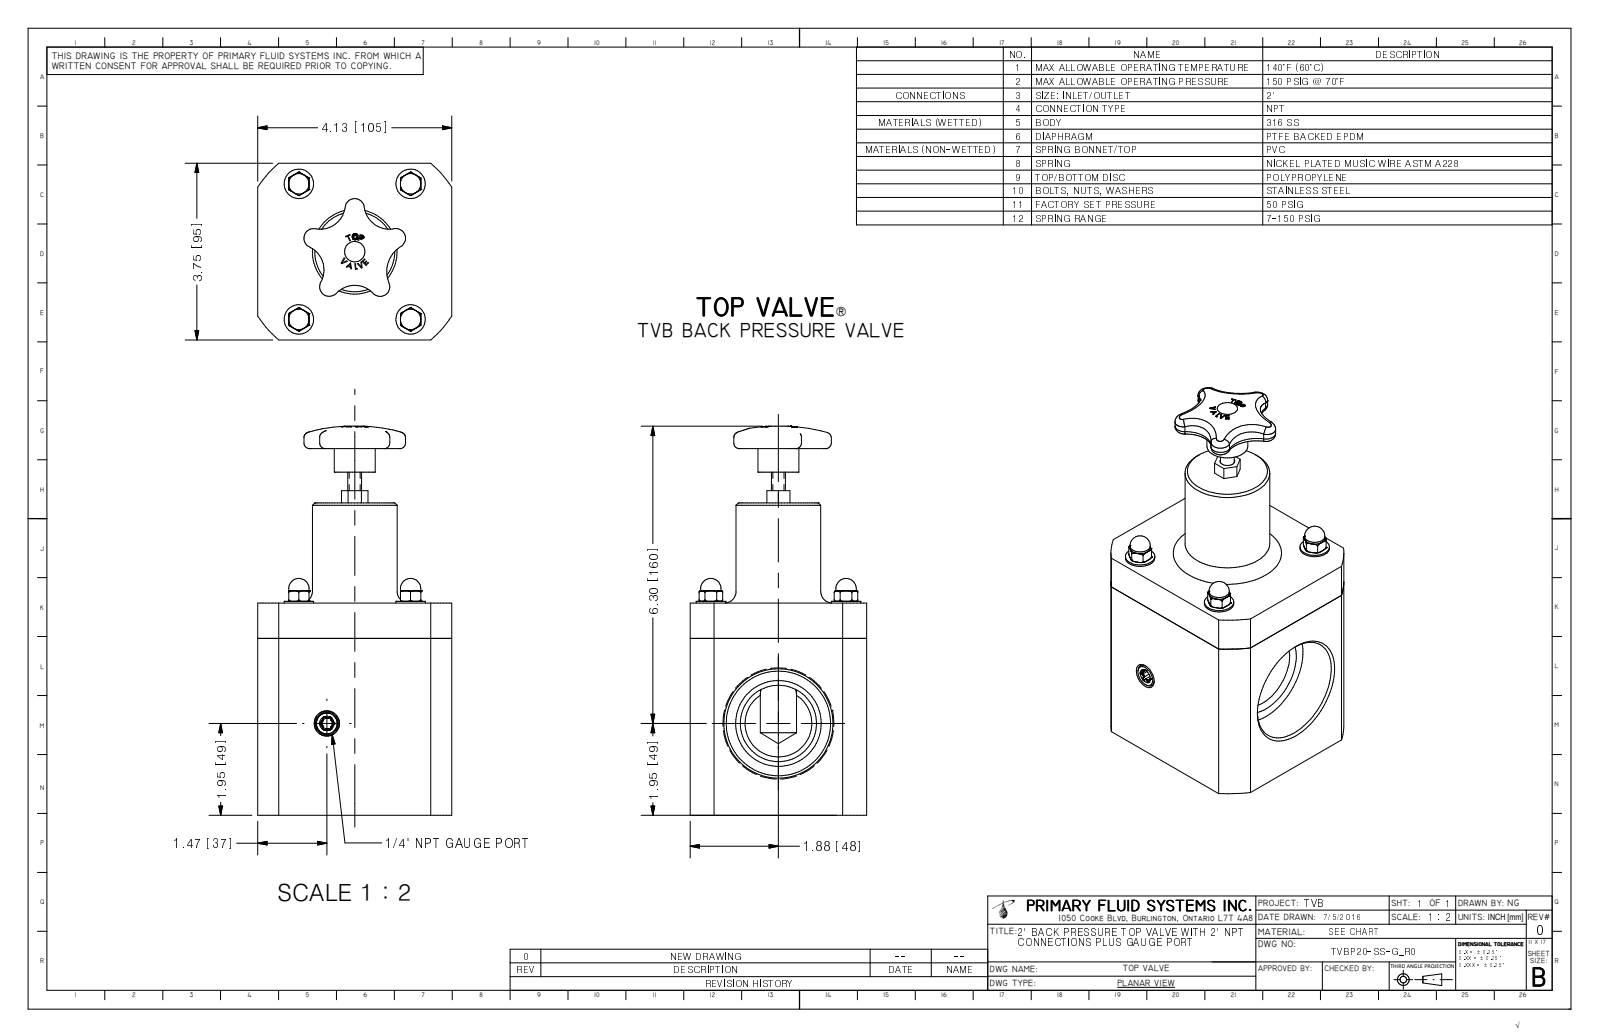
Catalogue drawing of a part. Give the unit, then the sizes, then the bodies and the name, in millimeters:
Units: millimetres
Overall size (bounding box): 209.6 × 104.8 × 95.3
Round holes (diameter × count): ⌀4.4 ×4, ⌀56.4 ×1
Round bosses / shafts (diameter × count): ⌀15.9 ×4, ⌀11 ×4, ⌀9.5 ×4, ⌀45.7 ×1, ⌀22.1 ×1, ⌀7.4 ×1
Partial cylindrical surfaces — rounded edges, fillets, slot ends (radius × count): R0.7 ×6, R2.2 ×5, R5.2 ×5, R13.6 ×4, R16.7 ×4, R15.9 ×1, R18.9 ×1, R62.9 ×1
Main face-to-face distances: 95.3, 114.3, 104.8, 22.9, 81.9, 59.1, 168.3, 54, 11, 115.2
Hole centre spacings: 60.3, 73, 94.7
Volume: 1 110 000 mm³ · Surface area: 87 680 mm²
Bodies: 1 solid, 359 faces (152 planar, 51 cylindrical, 156 other)
Part name (STEP PRODUCT): TVBP20-SS-G-R0
STEP written by: Autodesk Inventor 2009 (AUTOMOTIVE_DESIGN)
